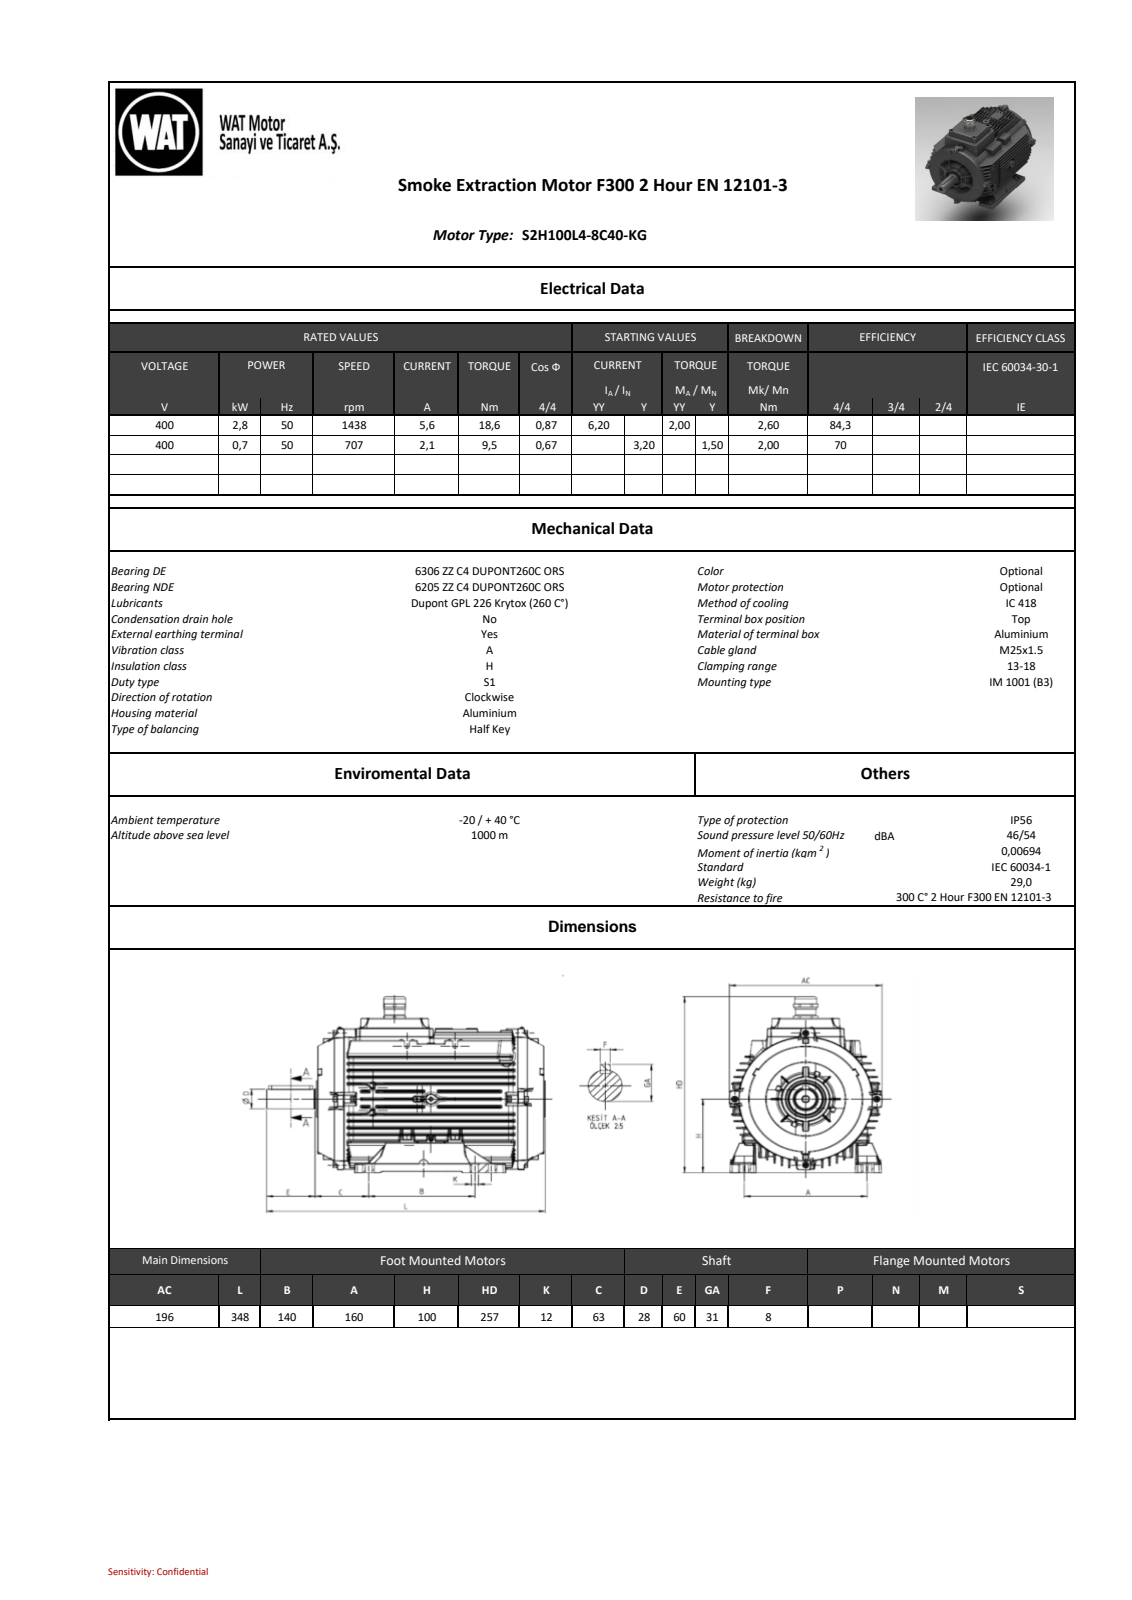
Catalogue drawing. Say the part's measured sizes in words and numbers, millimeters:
The part is named "260314206C66eb8i". Its 3-D file was written by "SIEMENS PLM Software NX 11.0 (AP203_CONFIGURATION_CONTROLLED_3D_DESIGN_OF_MECHANICAL_PARTS_AND_ASSEMBLIES_MIM_LF)". It is 0 solids with 6364 faces: 1240 planar, 1855 cylindrical and 3269 other. Overall it measures 348 by 257.2 by 196 millimeters. Round holes: 8 of diameter 6.5, 1 of diameter 8.5, 1 of diameter 10.5, 1 of diameter 18, 1 of diameter 32, 1 of diameter 40, 1 of diameter 43.9, 1 of diameter 44.1. Round bosses or shafts: 4 of diameter 9.2, 4 of diameter 8.5, 4 of diameter 8, 4 of diameter 5, 1 of diameter 168, 1 of diameter 30, 1 of diameter 29.59, 1 of diameter 28.14. Partial cylindrical surfaces (rounded edges, fillets, slot ends): 619 of radius 0.8, 301 of radius 1, 140 of radius 2, 94 of radius 0.5, 85 of radius 1.5, 59 of radius 0.81, 16 of radius 2.5, 16 of radius 4.5. The main face-to-face distances are 8.53, 8.46, 8.45, 76.24, 16.91, 93.45, 76.68, 17.05, 25.58, 59.63. The hole center spacings are 10, 64, 128, 128.39, 143.11, 54, 64.56, 66.62.
